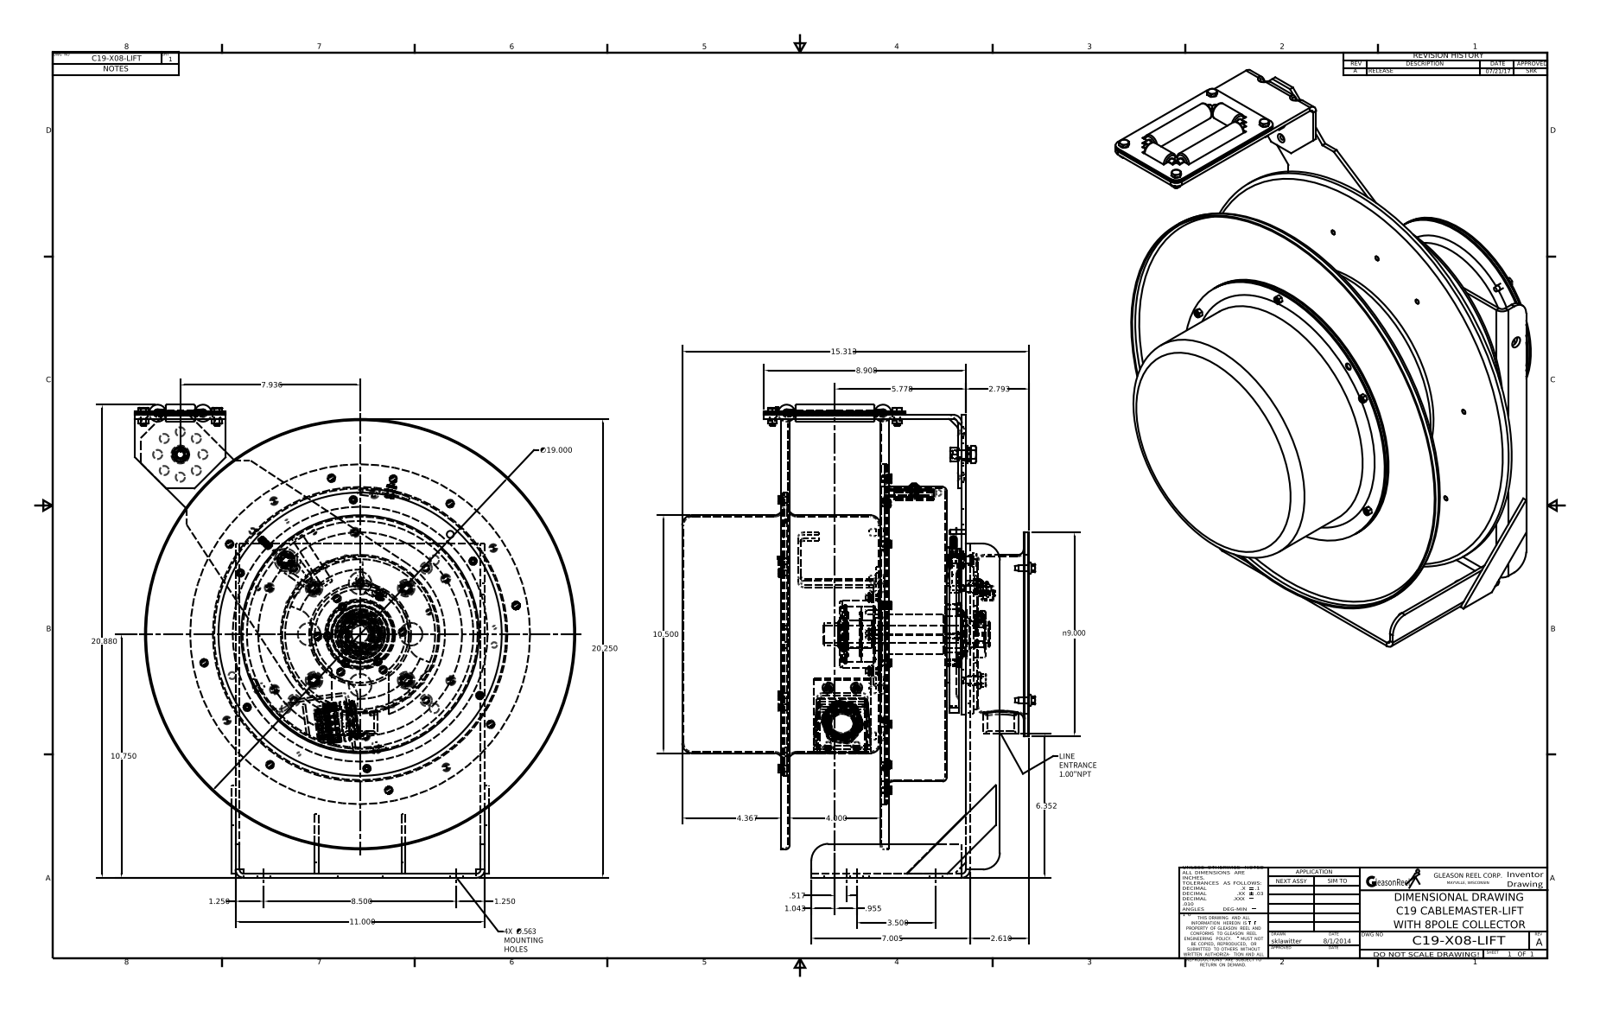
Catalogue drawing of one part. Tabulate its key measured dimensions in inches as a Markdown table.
| quantity | value |
| --- | --- |
| part name | C19-X08-LIFT (SW) |
| STEP written by | Autodesk Inventor 2016 (AUTOMOTIVE_DESIGN) |
| units | inches |
| bodies | 173 solids, 3480 faces (1373 planar, 1017 cylindrical, 1090 other) |
| overall size | 20.88 × 19.437 × 15.577 |
| volume | 236.2 in³ |
| surface area | 4 949 in² |
| round holes (diameter × count) | 0.25 × 31, 0.197 × 30, 0.163 × 26, 0.219 × 14, 0.406 × 13, 0.422 × 12, 0.156 × 7, 0.281 × 7, 0.199 × 6, 0.211 × 6, 0.224 × 6, 1 × 6 |
| round bosses / shafts (diameter × count) | 0.197 × 30, 0.236 × 10, 0.405 × 6, 0.394 × 6, 0.191 × 6, 0.5 × 5, 0.457 × 5, 0.315 × 5 |
| partial cylindrical surfaces (radius × count) | 0.03 × 67, 0.01 × 64, 0.015 × 41, 0.078 × 18, 0.006 × 12, 0.06 × 12, 0.124 × 8, 0.125 × 7 |
| main face-to-face distances | 0.06, 0.185, 0.179, 0.245, 0.125, 4.305, 4.12, 4.06, 2.687, 2.872 |
| hole center spacings | 1.25, 0.765, 1, 1.414, 1.848, 4.063, 5.443, 5.446 |
